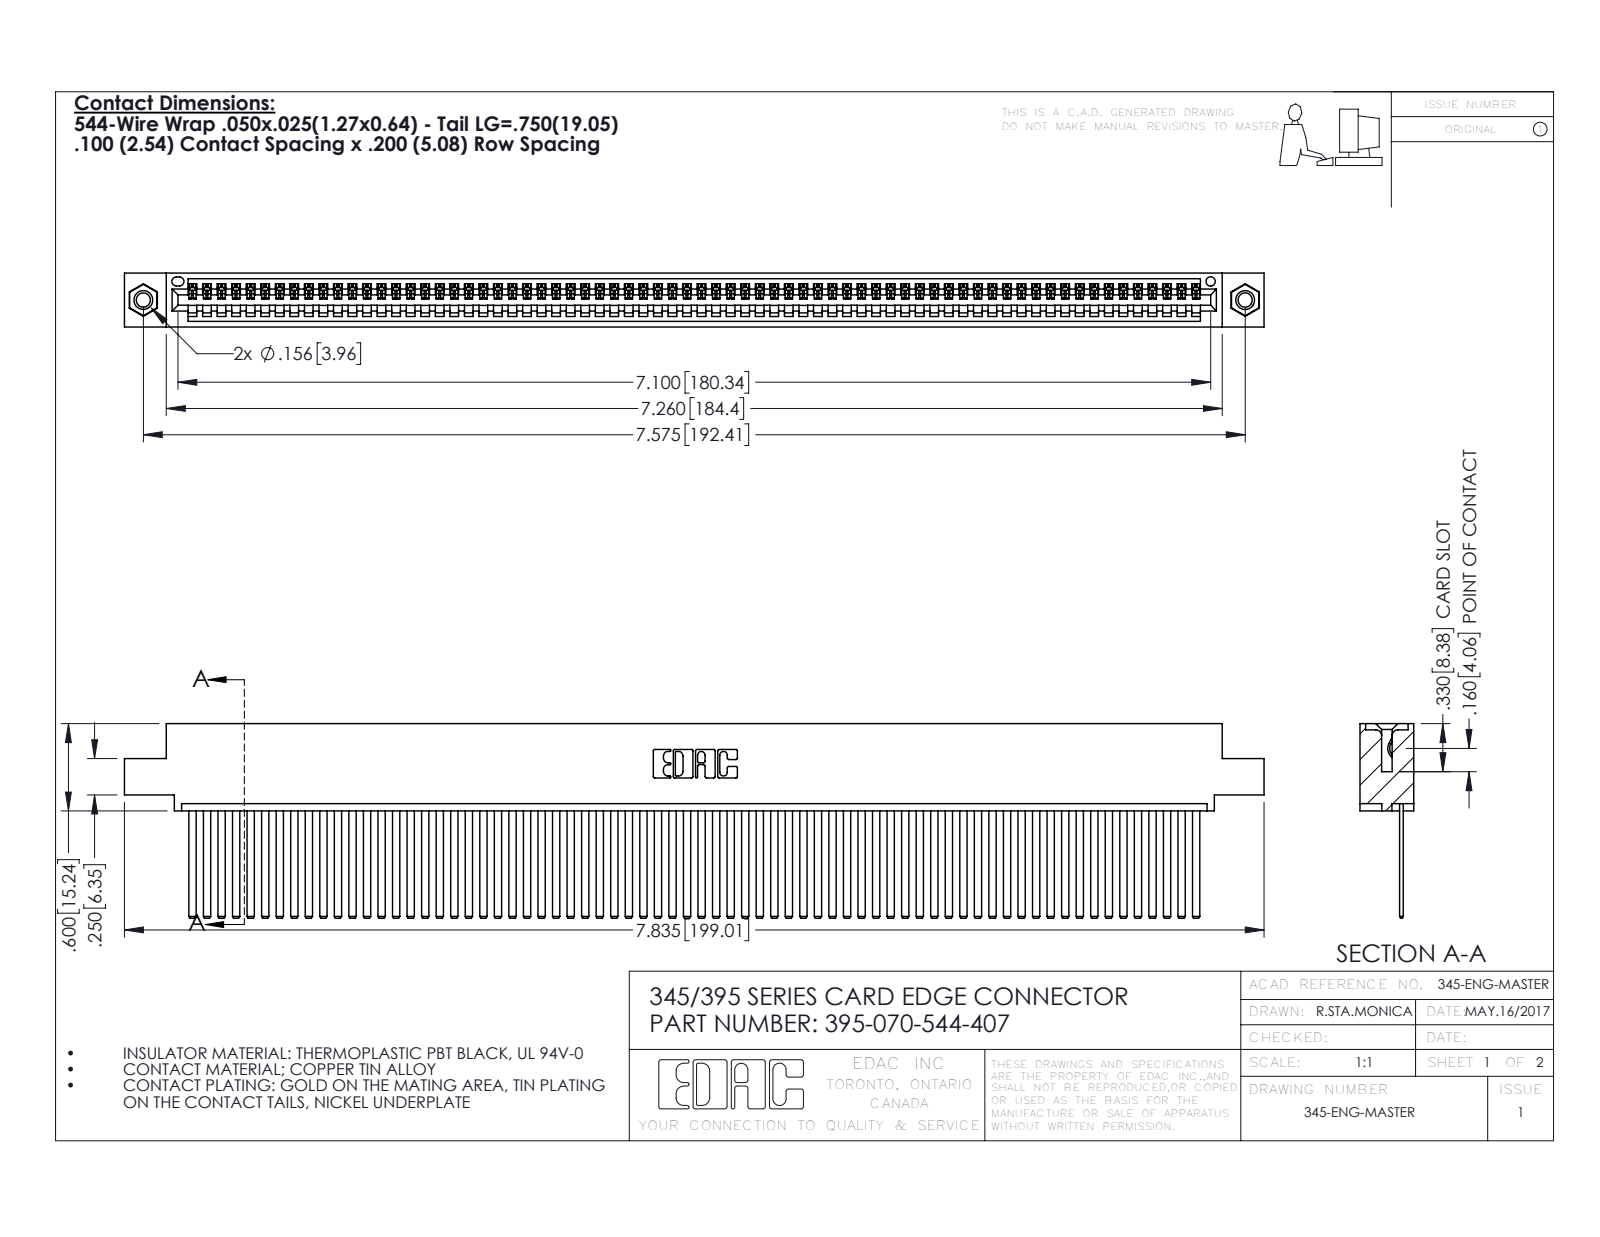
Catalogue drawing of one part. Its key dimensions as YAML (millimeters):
part_name: "345 Part_0.110 Offset - 0.156 Dia-TI; 345-292-001_345-293-144; 395-070-544-407; 345-250-001_345-250-005-103"
step_written_by: "SolidWorks 2016 (CONFIG_CONTROL_DESIGN)"
units: millimeters
bodies: {solids: 73, faces: 3830, planar: 2636, cylindrical: 1178, other: 16}
overall_size: [199, 34, 9.4]
volume: 19860
surface_area: 29320
round_holes:
  - {diameter: 2.5, count: 2}
  - {diameter: 3.2, count: 2}
  - {diameter: 4, count: 2}
  - {diameter: 1.6, count: 1}
round_bosses_or_shafts:
  - {diameter: 3.9, count: 2}
partial_cylinders:
  - {radius: 0.2, count: 140}
  - {radius: 0.3, count: 22}
  - {radius: 0.2, count: 6}
  - {radius: 0.8, count: 6}
  - {radius: 0.7, count: 3}
  - {radius: 0.8, count: 2}
  - {radius: 1, count: 2}
  - {radius: 0.4, count: 1}
face_to_face_distances: [1.8, 7.6, 0.6, 2.5, 6.9, 9.4, 5.1, 5.7, 3.8, 1.8]
hole_center_spacings: [6.9, 186.4, 192.4]
